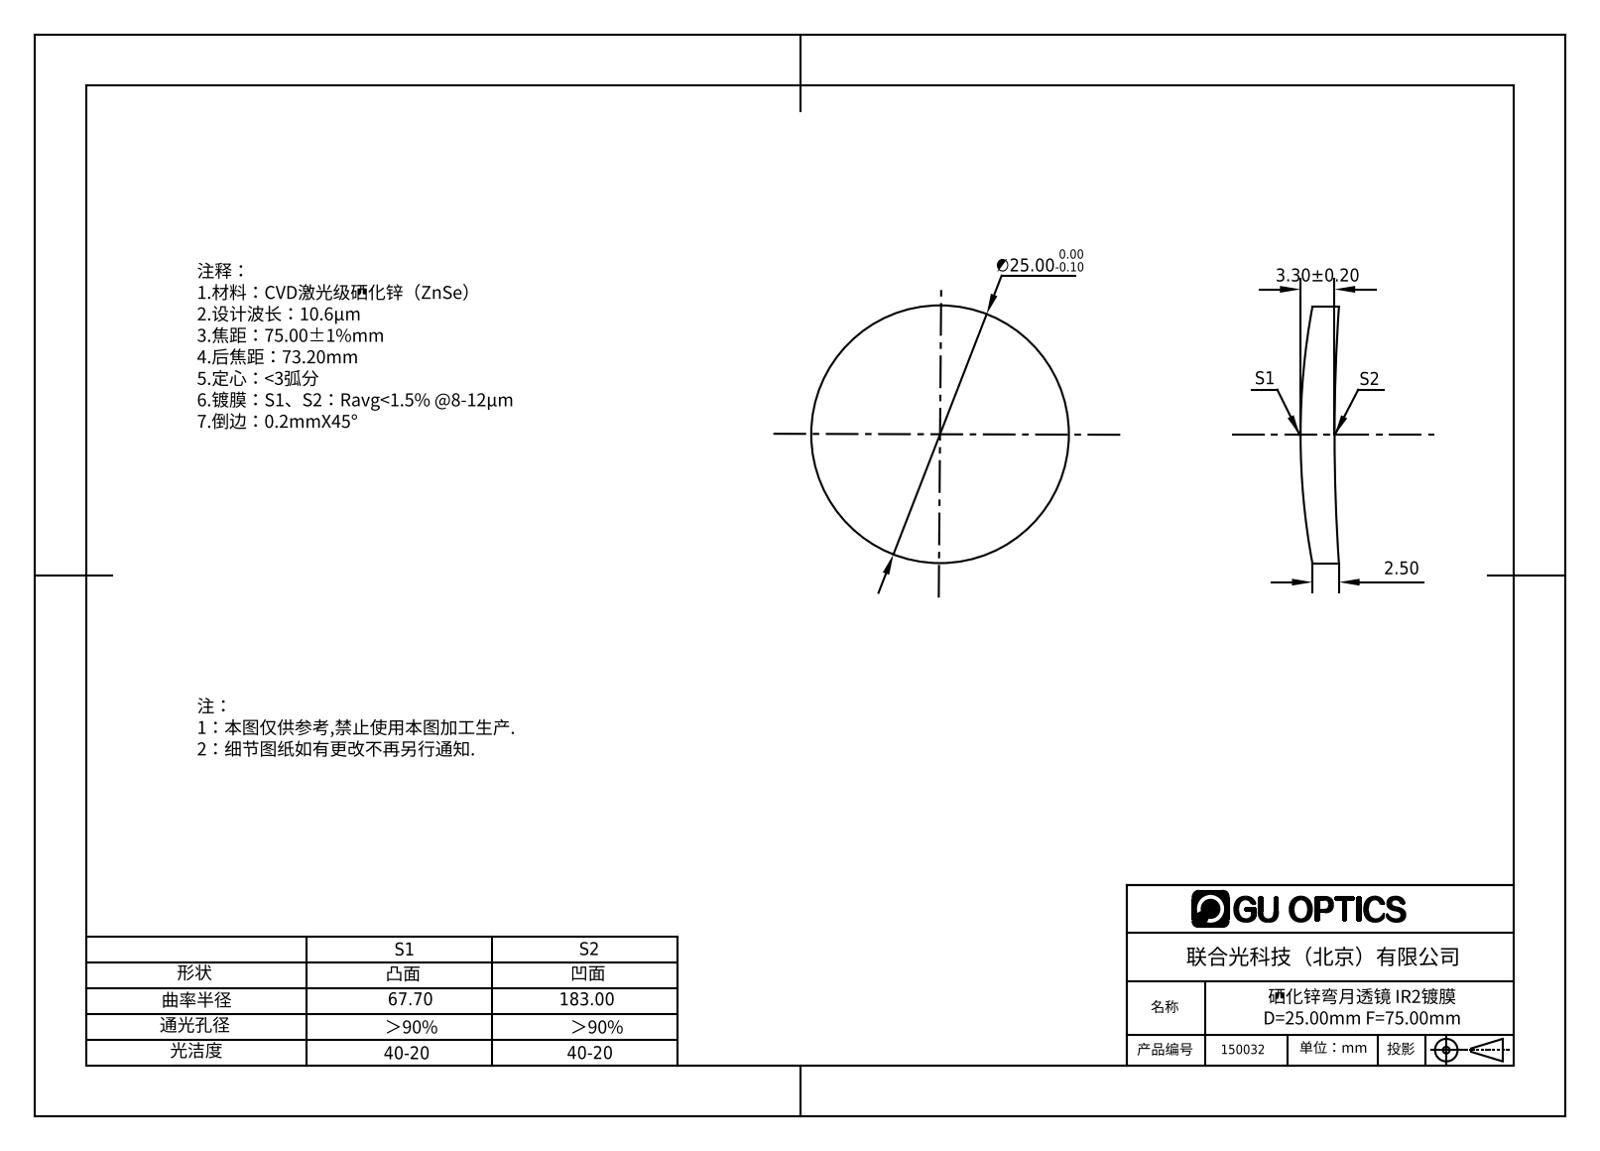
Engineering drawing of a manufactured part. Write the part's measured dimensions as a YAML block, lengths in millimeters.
part_name: "150007"
step_written_by: "SolidWorks 2016 (AUTOMOTIVE_DESIGN)"
units: millimeters
bodies: {solids: 1, faces: 6, planar: 0, cylindrical: 2, other: 4}
overall_size: [25, 25, 3.73]
volume: 1440
surface_area: 1188
round_bosses_or_shafts:
  - {diameter: 25, count: 1}
